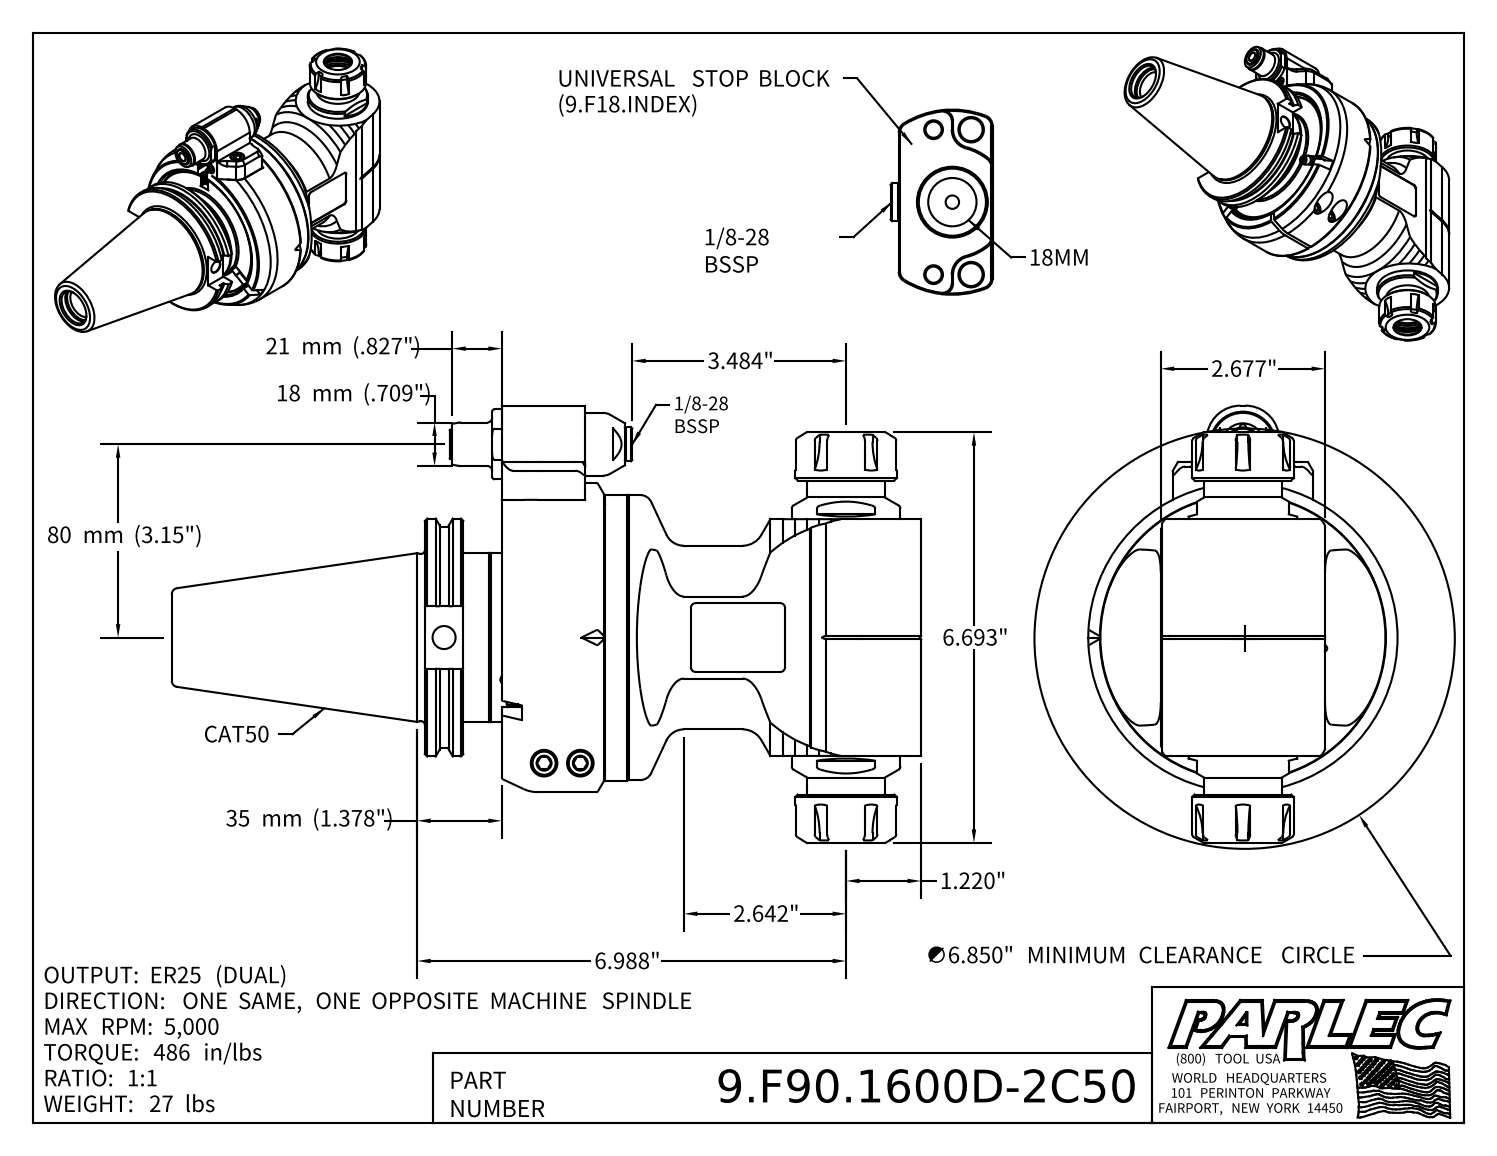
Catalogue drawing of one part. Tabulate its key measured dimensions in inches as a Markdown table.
| quantity | value |
| --- | --- |
| part name | 9.F90.1600D-2C50; 9_F90_16_2U0; 9GA21C_458 |
| STEP written by | Autodesk Inventor 2025 (AUTOMOTIVE_DESIGN) |
| units | inches |
| bodies | 4 solids, 712 faces (326 planar, 179 cylindrical, 207 other) |
| overall size | 12.209 × 7.126 × 5.039 |
| volume | 110 in³ |
| surface area | 329.5 in² |
| round holes (diameter × count) | 0.079 × 4, 0.197 × 3, 0.256 × 3, 0.492 × 3, 0.102 × 2, 0.13 × 2, 0.165 × 2, 0.315 × 2, 0.409 × 2, 0.433 × 2, 0.512 × 2, 1.063 × 2 |
| round bosses / shafts (diameter × count) | 0.394 × 4, 0.709 × 2, 0.472 × 2, 0.236 × 2, 0.098 × 2, 5.039 × 1, 4.661 × 1, 4.646 × 1 |
| partial cylindrical surfaces (radius × count) | 0.039 × 14, 0.079 × 12, 0.984 × 12, 0.118 × 6, 0.157 × 4, 0.016 × 2, 0.02 × 2, 0.138 × 2 |
| main face-to-face distances | 1.398, 0.256, 1.339, 0.079, 0.02, 0.197, 0.059, 0.335, 1.417, 1.594 |
| hole center spacings | 1.093, 0.276, 0.504, 0.74, 0.996, 1.391, 1.545, 1.545 |
